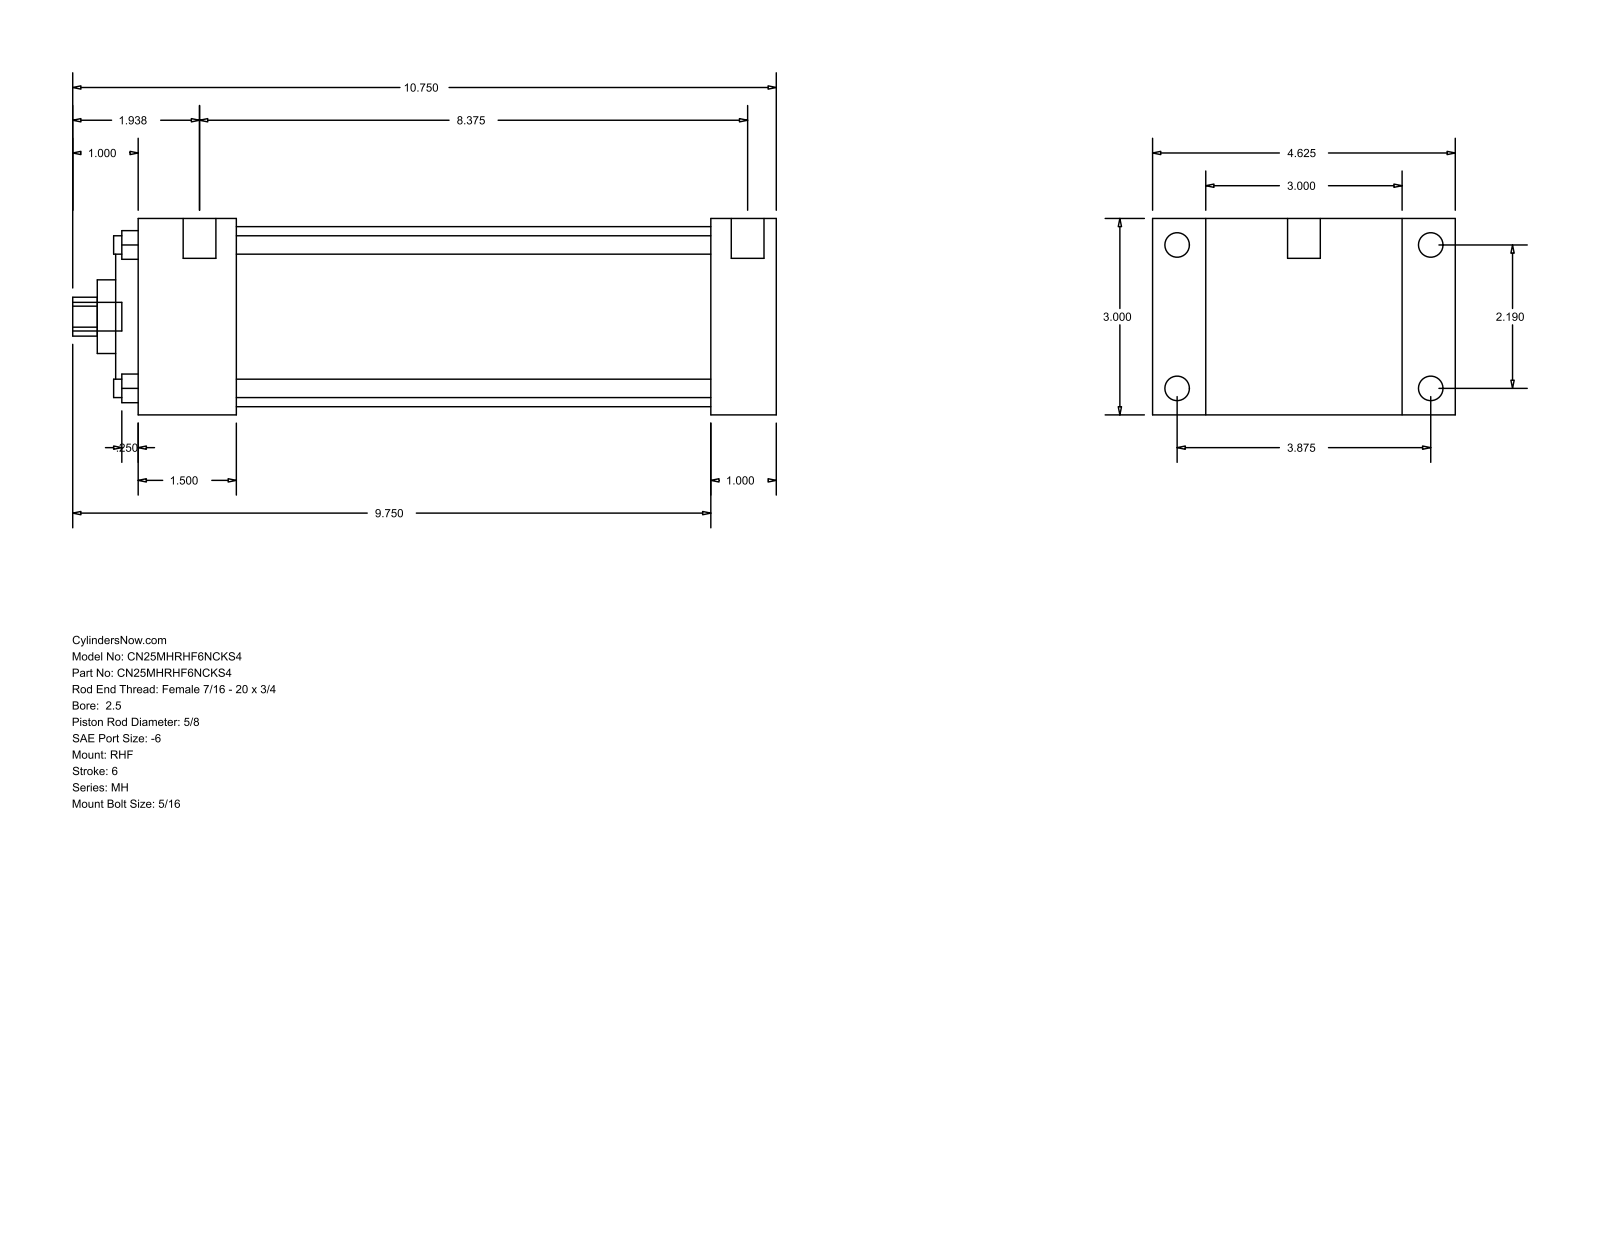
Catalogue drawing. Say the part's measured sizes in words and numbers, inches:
The part is named "MH_RHF__0250_0.625". Its 3-D file was written by "GSSL Pune (CONFIG_CONTROL_DESIGN)". It is 0 solids with 90 faces: 61 planar, 29 cylindrical and 0 other. Overall it measures 10.75 by 4.625 by 3 inches. Round holes: 4 of diameter 0.281, 1 of diameter 0.625, 1 of diameter 1.125, 1 of diameter 2.187, 1 of diameter 2.75. Round bosses or shafts: 4 of diameter 0.375, 4 of diameter 0.219, 2 of diameter 0.5, 1 of diameter 0.437. Partial cylindrical surfaces (rounded edges, fillets, slot ends): 1 of radius 0.297. The main face-to-face distances are 3, 1, 0.813, 3.813, 9.75, 8.75, 4.625, 1.5, 7.25, 8.25. The hole center spacings are 1.548, 2.19, 3.097.
